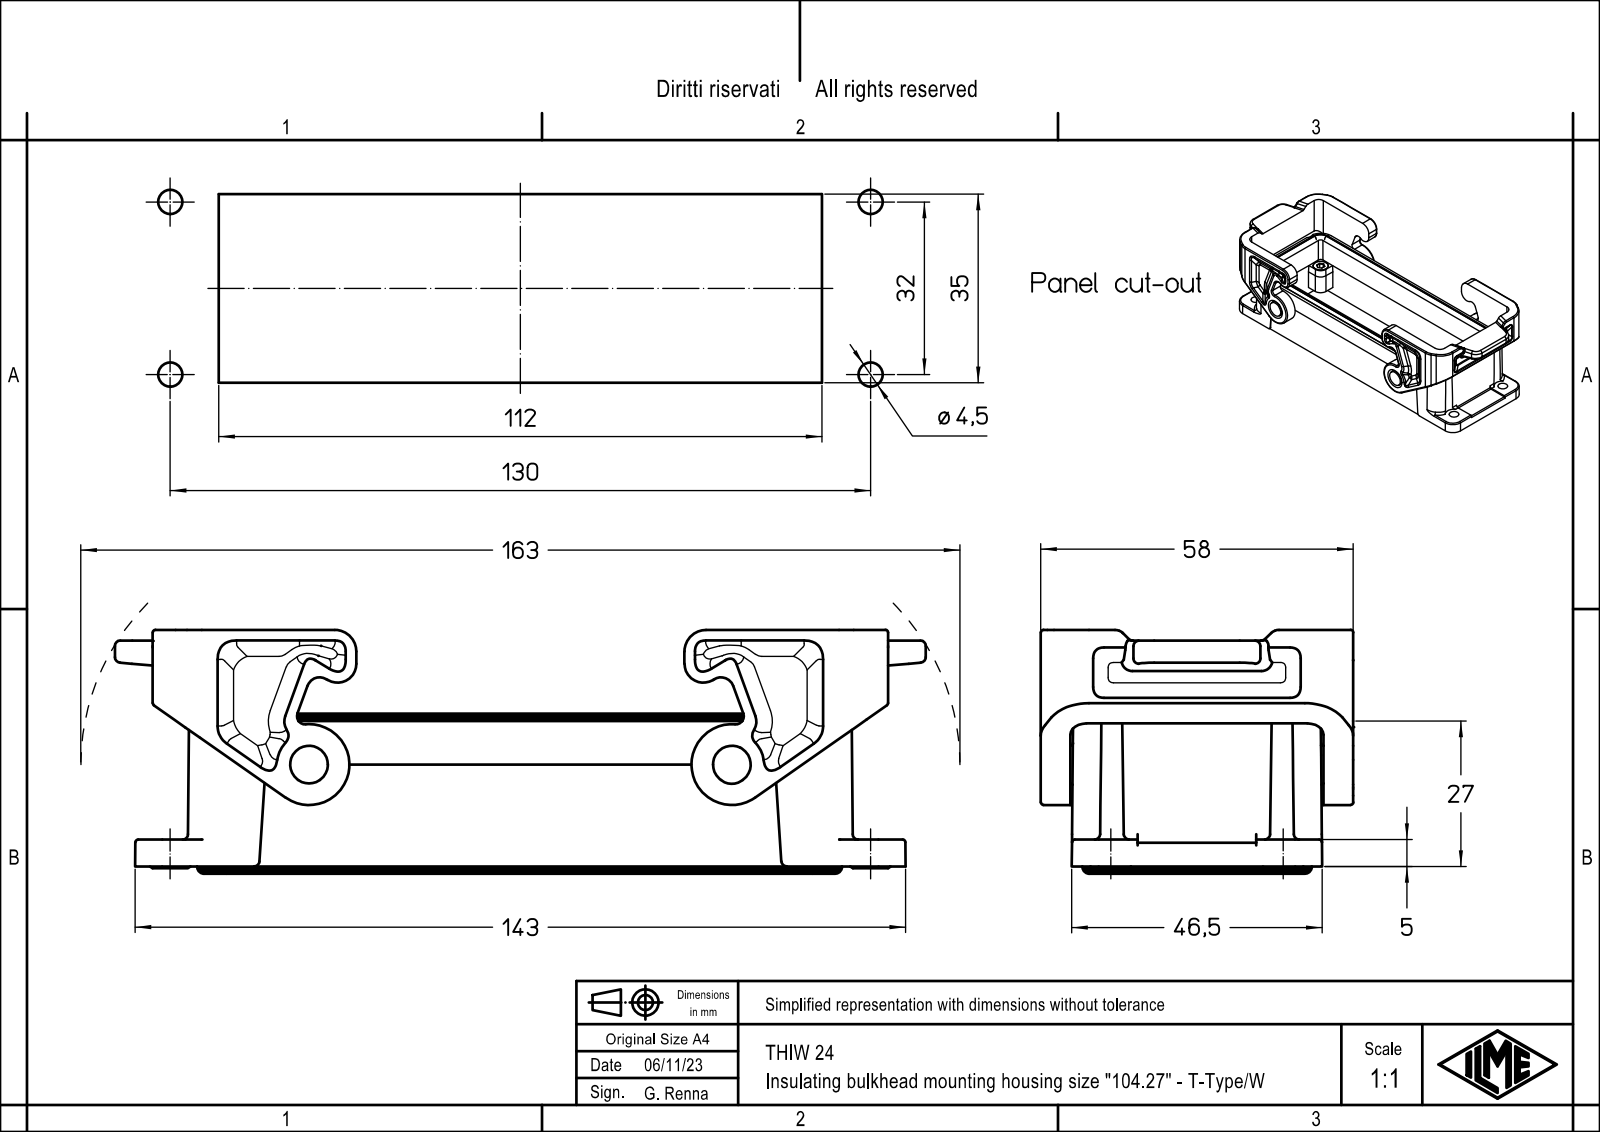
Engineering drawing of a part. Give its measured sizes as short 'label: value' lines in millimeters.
name: THIW 24
written by: Creo Elements/Direct Modeling 20.1B 02-Apr-2019 (C) Parametric Technology GmbH (AUTOMOTIVE_DESIGN)
unit: mm
bodies: 1 solid, 714 faces (310 planar, 220 cylindrical, 184 other)
size: 150.5 × 58 × 45.25
volume: 78 302 mm³; area: 41 694 mm²
holes: 4× ⌀2.5, 4× ⌀4.5, 2× ⌀7.2
bosses: 4× ⌀4.8, 2× ⌀7
rounds: 28× R1, 16× R1.3, 14× R1.5, 12× R2, 12× R3, 12× R5.5, 10× R2.7, 8× R5
face distances: 5.9, 41.1, 35.2, 5.5, 52.5, 11.4, 46.6, 47, 7.15, 119.35
hole spacings: 13.24, 32.24, 117.03, 120.66, 27, 32, 104, 107.45
